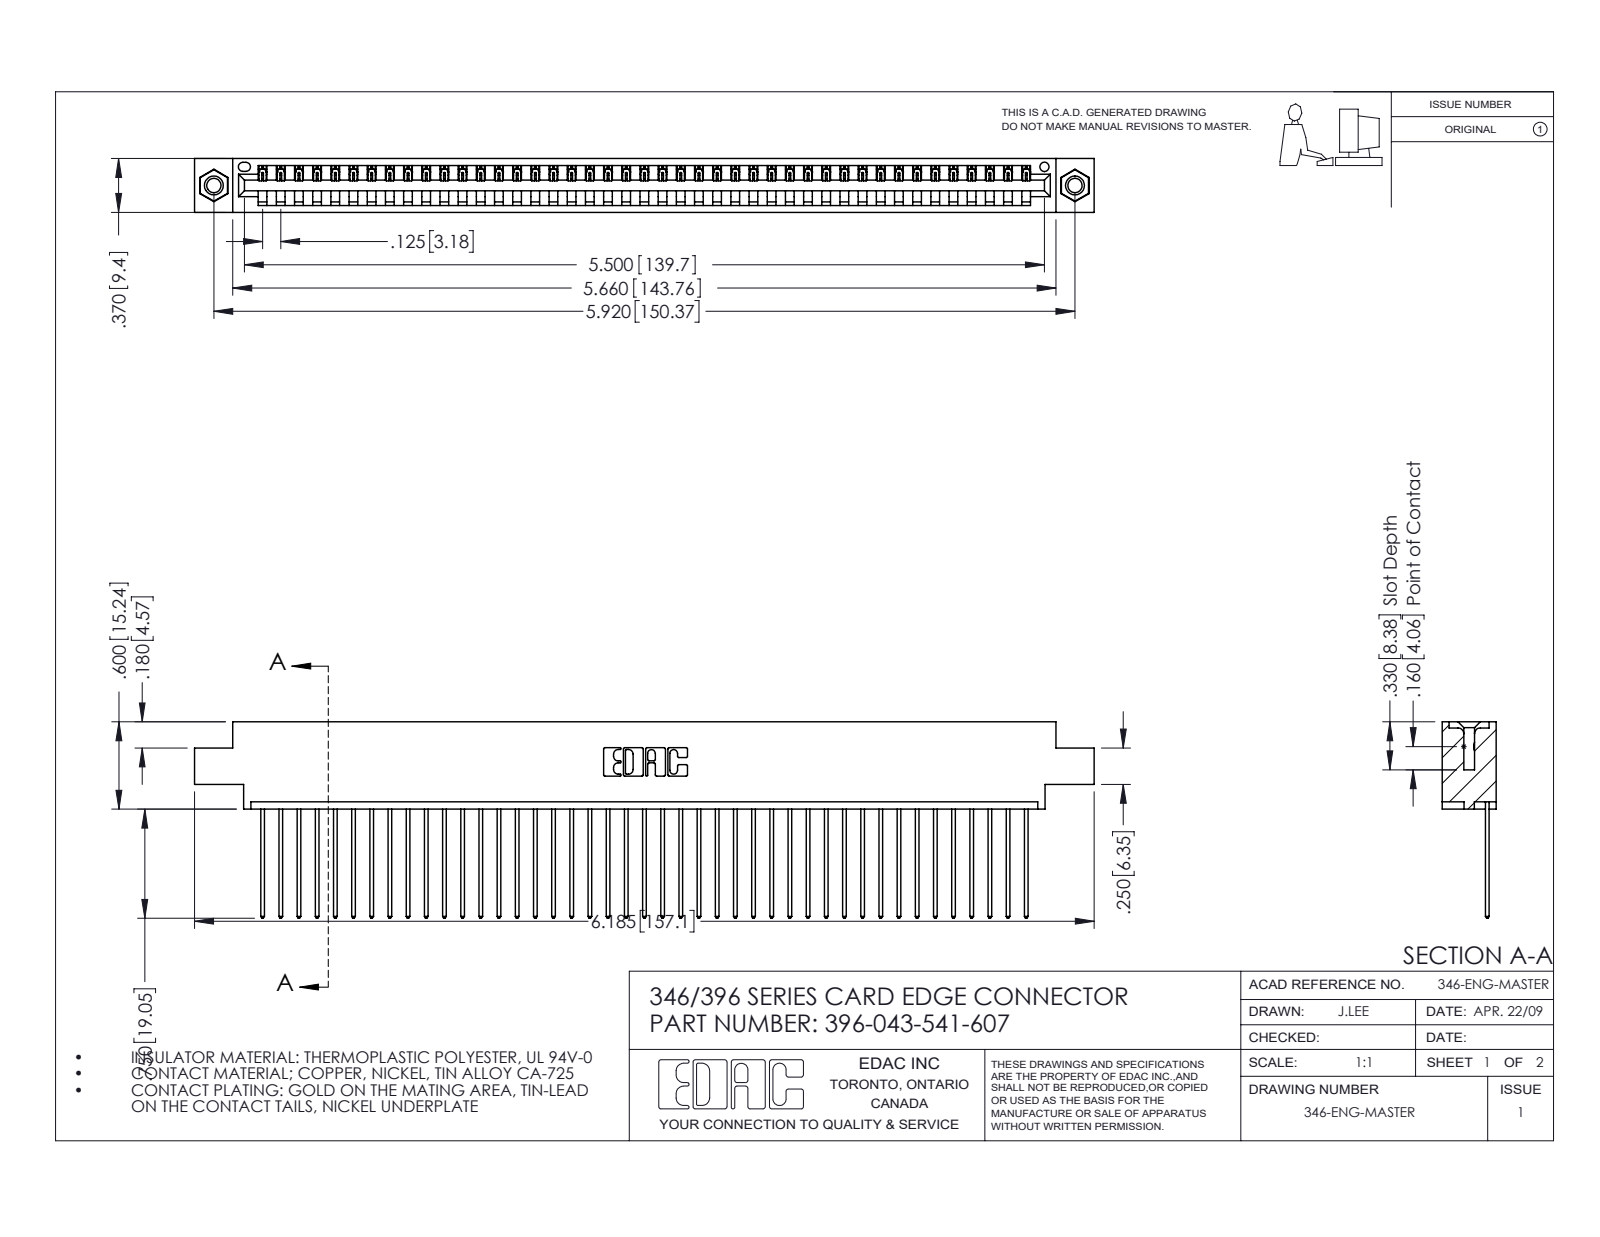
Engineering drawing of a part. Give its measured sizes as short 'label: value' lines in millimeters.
name: 345-250-001_345-250-005-103; 345-292-001_345-293-141; 346 Part_0.170 Offset - 0.156 Dia-TI; 396-043-541-607
written by: SolidWorks 2016 (CONFIG_CONTROL_DESIGN)
unit: mm
bodies: 46 solids, 2680 faces (1832 planar, 832 cylindrical, 16 other)
size: 157.1 × 34.3 × 9.4
volume: 15 000 mm³; area: 19 830 mm²
holes: 2× ⌀2.5, 2× ⌀3.2, 2× ⌀4, 1× ⌀1.6
bosses: 2× ⌀3.9
rounds: 86× R0.2, 86× R0.3, 22× R0.3, 6× R0.2, 6× R0.8, 3× R0.7, 2× R0.8, 2× R1
face distances: 1.2, 8.2, 9.4, 6.4, 1.8, 7.6, 0.6, 5.6, 3.8, 2.5
hole spacings: 6.2, 145.1, 150.4
